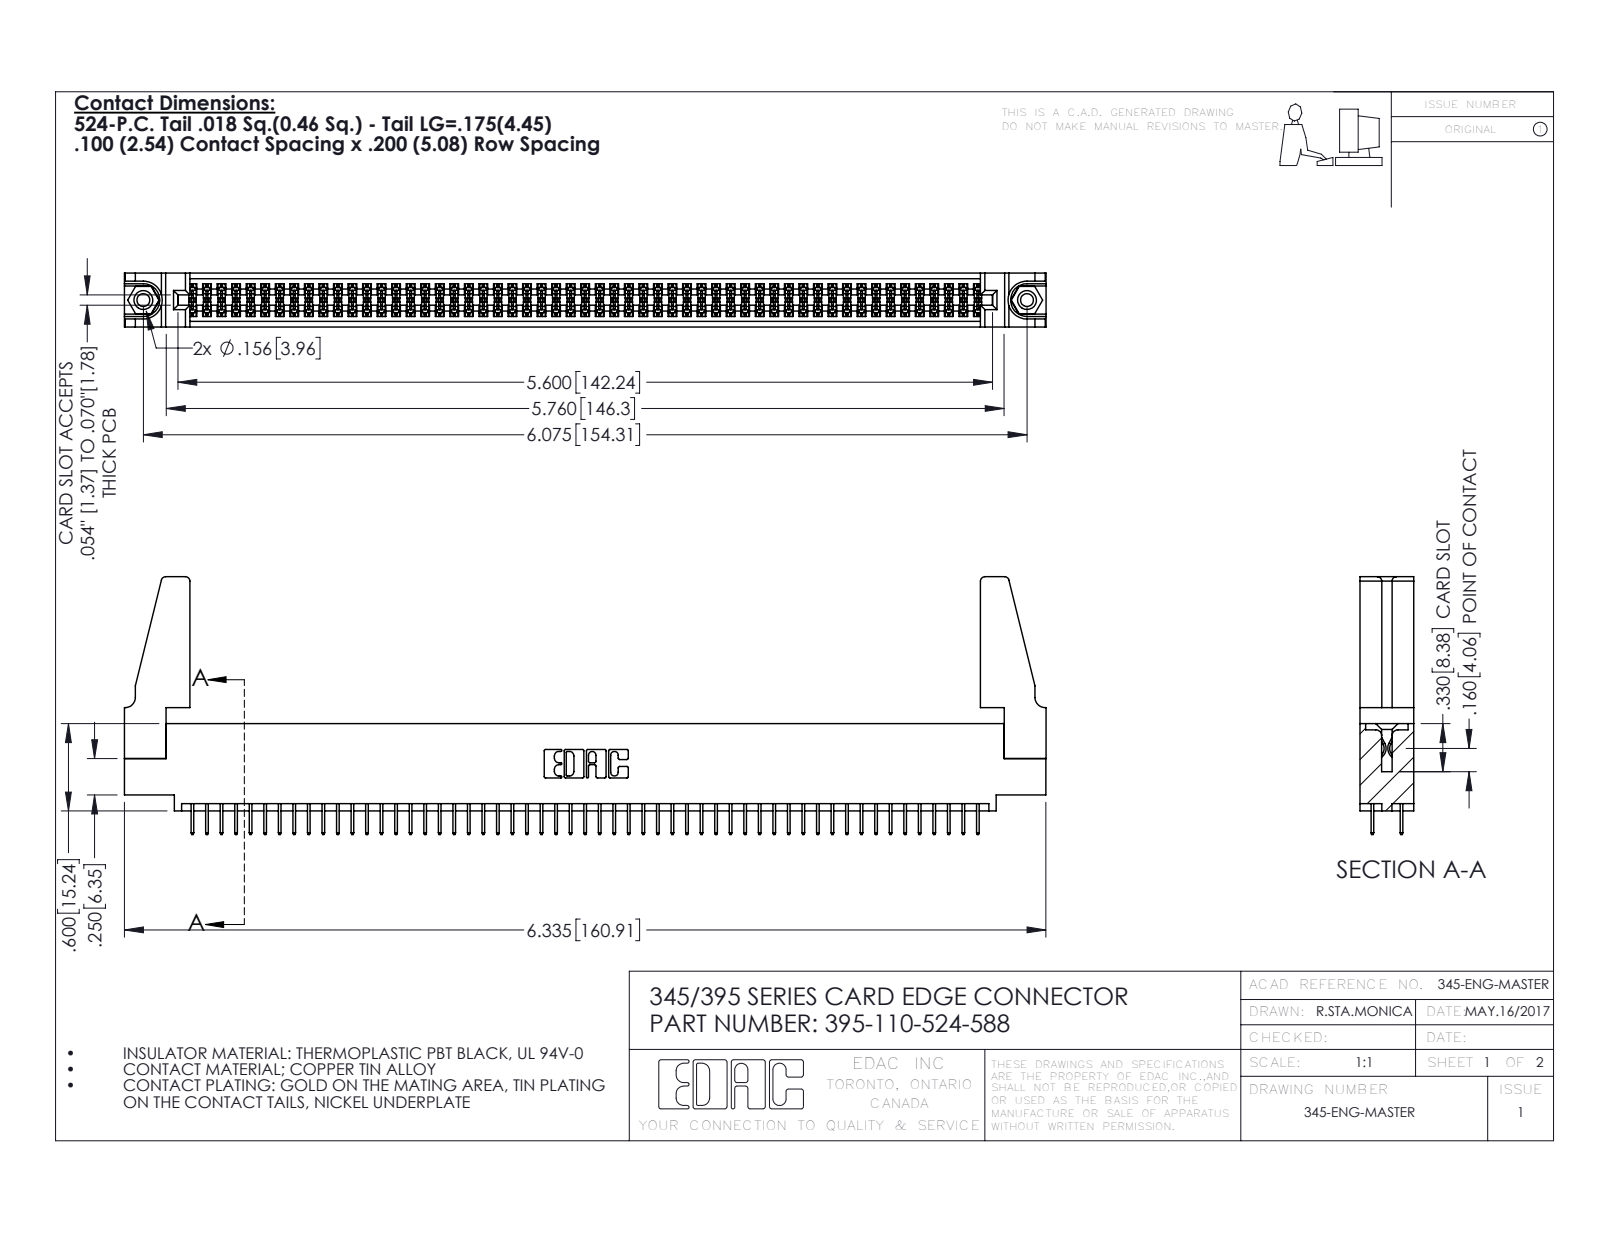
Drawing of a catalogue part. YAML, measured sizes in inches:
part_name: "395-110-524-588; 345-220-078_345-220-088; 345-250-001_345-250-001-102; 345 Part_0.110 Offset - 0.156 Dia-TH (+1 more)"
step_written_by: "SolidWorks 2016 (CONFIG_CONTROL_DESIGN)"
units: inches
bodies: {solids: 115, faces: 6194, planar: 4446, cylindrical: 1732, other: 16}
overall_size: [6.336, 1.772, 0.37]
volume: 1.145
surface_area: 40.24
round_holes:
  - {diameter: 0.089, count: 2}
  - {diameter: 0.125, count: 2}
  - {diameter: 0.156, count: 2}
  - {diameter: 0.064, count: 1}
round_bosses_or_shafts:
  - {diameter: 0.155, count: 2}
partial_cylinders:
  - {radius: 0.006, count: 165}
  - {radius: 0.01, count: 22}
  - {radius: 0.03, count: 8}
  - {radius: 0.007, count: 6}
  - {radius: 0.031, count: 6}
  - {radius: 0.026, count: 3}
  - {radius: 0.014, count: 2}
  - {radius: 0.019, count: 2}
face_to_face_distances: [0.072, 0.298, 0.37, 0.2, 0.098, 0.272, 0.025, 0.225, 0.072, 0.175]
hole_center_spacings: [0.27, 5.839, 6.075]
